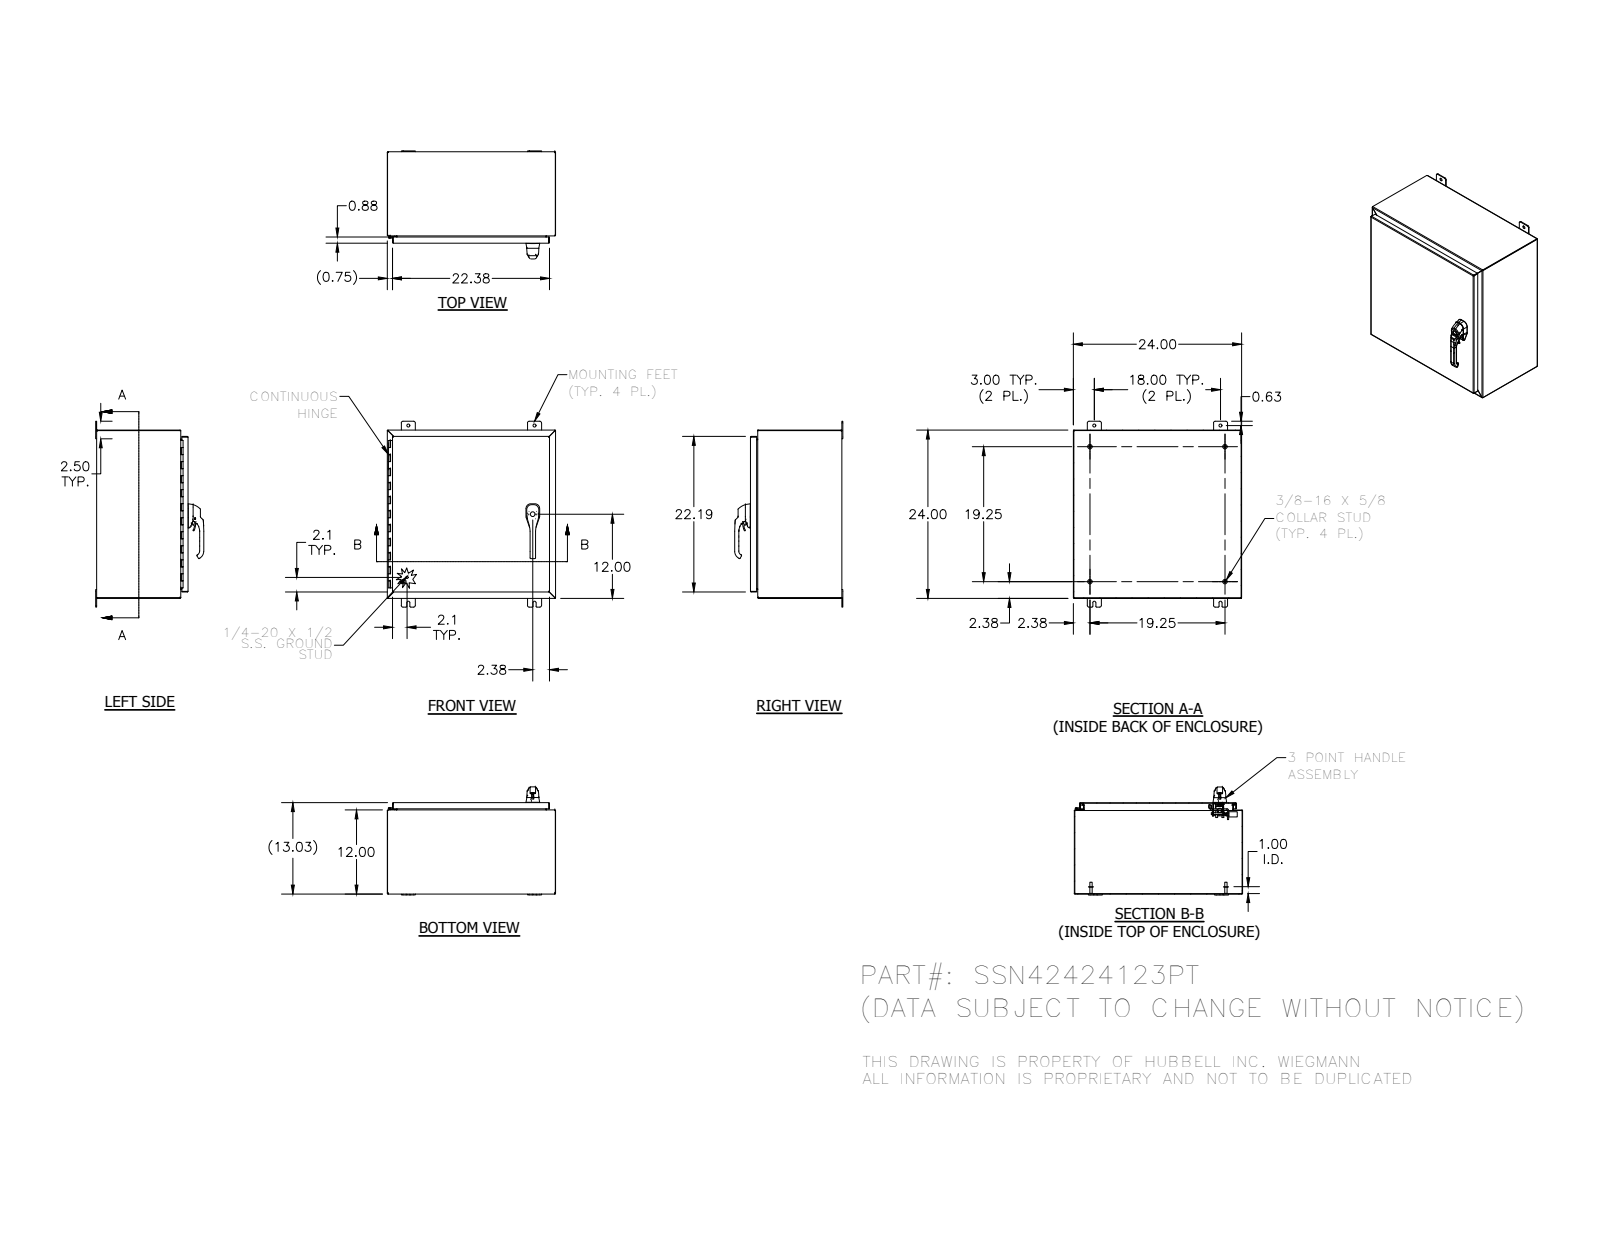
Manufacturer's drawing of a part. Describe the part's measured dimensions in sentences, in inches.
The part is named "328138; 31230; 1091-903_AF0_1; DIN3771_16X2_5 (+8 more)". Its 3-D file was written by "SolidWorks 2014 (AUTOMOTIVE_DESIGN)". It is 56 solids with 3059 faces: 1014 planar, 1260 cylindrical and 785 other. Overall it measures 26.5 by 24 by 15.408 inches. Its volume is 212.5 cubic inches and its surface area 5 495 square inches. Round holes: 8 of diameter 0.262, 4 of diameter 0.187, 4 of diameter 0.438, 3 of diameter 0.213, 3 of diameter 0.281, 2 of diameter 0.241, 2 of diameter 0.25, 2 of diameter 0.252, 2 of diameter 0.315, 2 of diameter 0.4, 2 of diameter 0.402, 2 of diameter 0.413. Round bosses or shafts: 4 of diameter 0.625, 4 of diameter 0.33, 3 of diameter 0.236, 2 of diameter 1, 2 of diameter 0.563, 2 of diameter 0.533, 2 of diameter 0.531, 2 of diameter 0.5. Partial cylindrical surfaces (rounded edges, fillets, slot ends): 172 of radius 0.02, 113 of radius 0.012, 26 of radius 0.125, 24 of radius 0.031, 21 of radius 0.019, 20 of radius 0.105, 20 of radius 0.25, 16 of radius 0.025. The main face-to-face distances are 0.074, 23.926, 12.959, 23.852, 24, 12.885, 13.033, 11.926, 1.033, 12. The hole center spacings are 0.38, 0.492, 0.76, 0.886, 14.428, 0.234, 0.258, 0.38.
